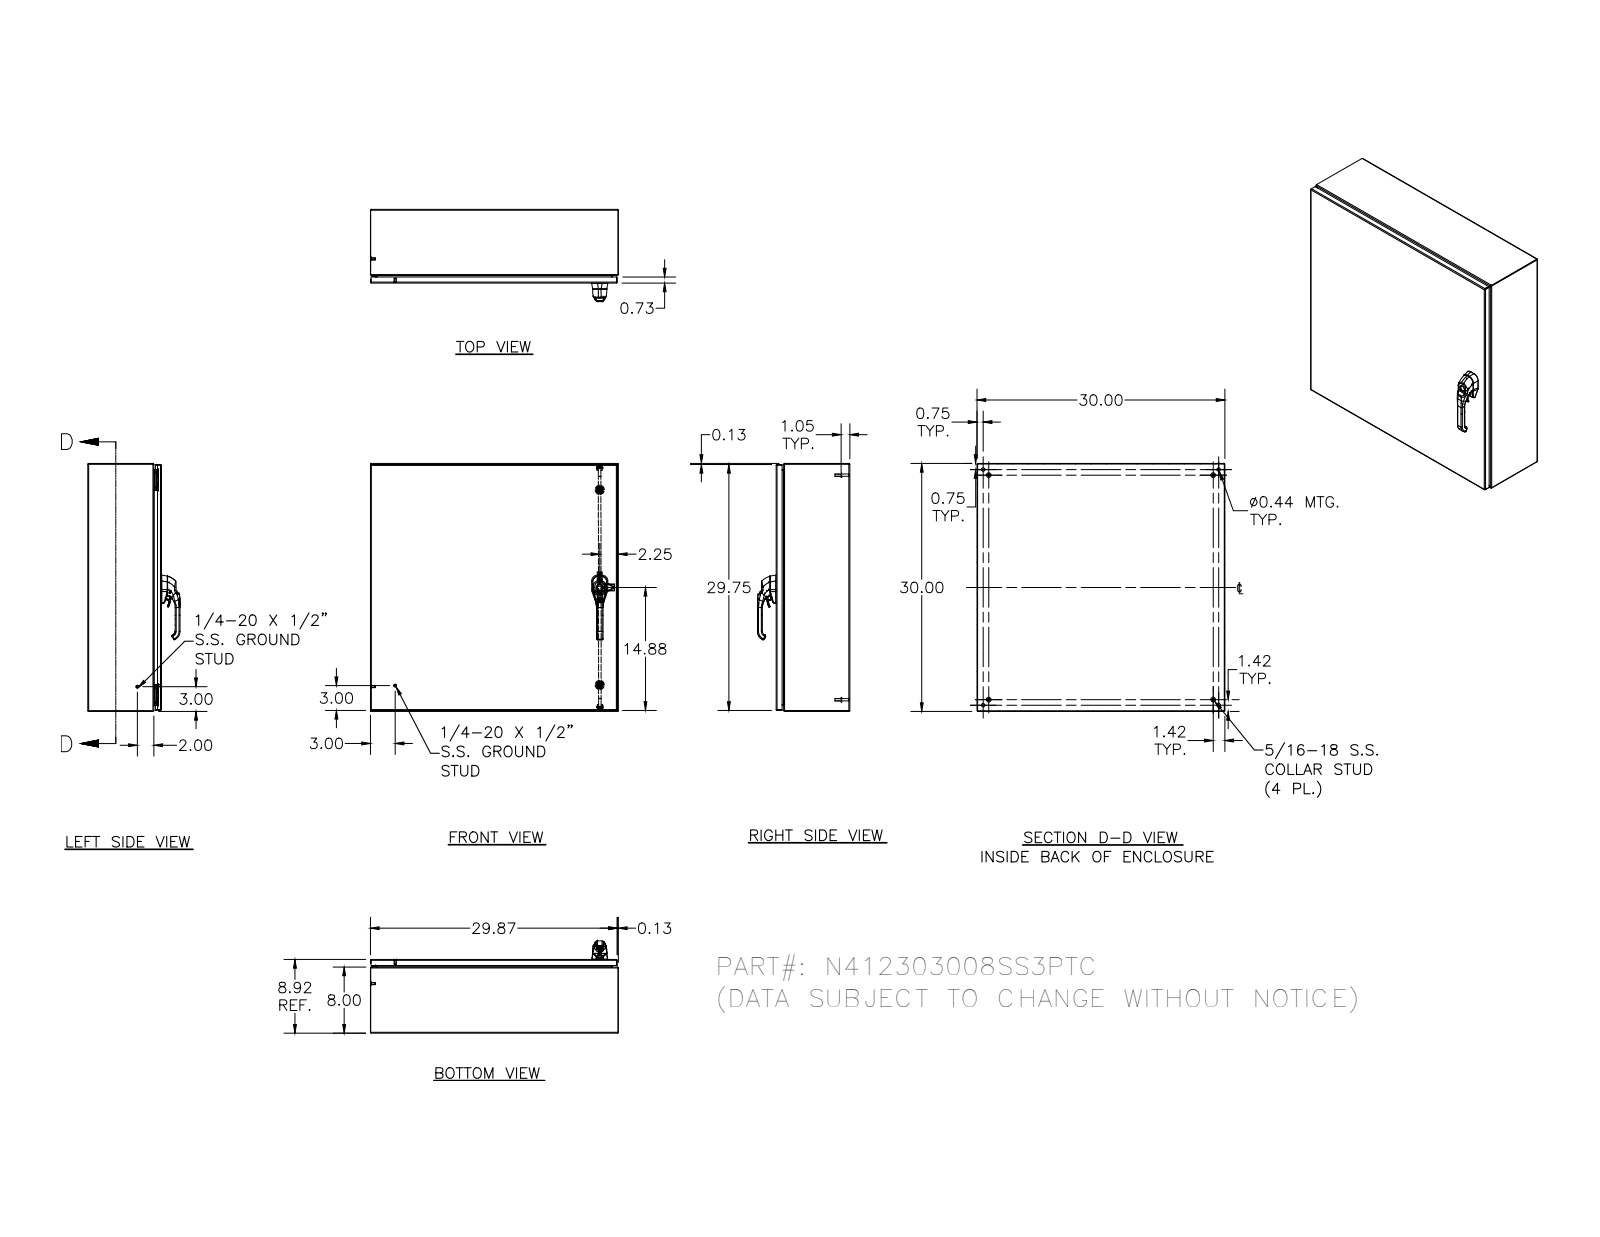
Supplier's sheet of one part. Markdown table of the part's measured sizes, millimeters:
| quantity | value |
| --- | --- |
| part name | N412303008SS3PTC; N412303008SS3PTCBKP; N4123030SS3PTCLID; HFW328176 (+8 more) |
| STEP written by | Autodesk Inventor 2011 (AUTOMOTIVE_DESIGN) |
| units | millimeters |
| bodies | 63 solids, 3086 faces (1046 planar, 1117 cylindrical, 923 other) |
| overall size | 762 × 762 × 283.6 |
| volume | 3 812 000 mm³ |
| surface area | 3 975 000 mm² |
| round holes (diameter × count) | 4.2 × 6, 2.4 × 4, 3.9 × 4, 4.2 × 4, 4.4 × 4, 4.8 × 4, 5 × 4, 11.1 × 4, 5.4 × 3, 2.7 × 2, 4 × 2, 4.1 × 2 |
| round bosses / shafts (diameter × count) | 6.4 × 10, 6 × 6, 15 × 5, 14.3 × 4, 9.1 × 4, 8.1 × 4, 7.9 × 4, 7.6 × 4 |
| partial cylindrical surfaces (radius × count) | 0.5 × 188, 0.3 × 100, 0.8 × 30, 1.3 × 26, 0.5 × 23, 3 × 23, 2.7 × 20, 0.4 × 18 |
| main face-to-face distances | 1.9, 224.6, 760.1, 226.5, 222.7, 758.2, 762, 201.3, 23.3, 18.8 |
| hole center spacings | 660.3, 695.8, 723.9, 0.4, 16.8, 41.1, 677.1, 0.5 |
